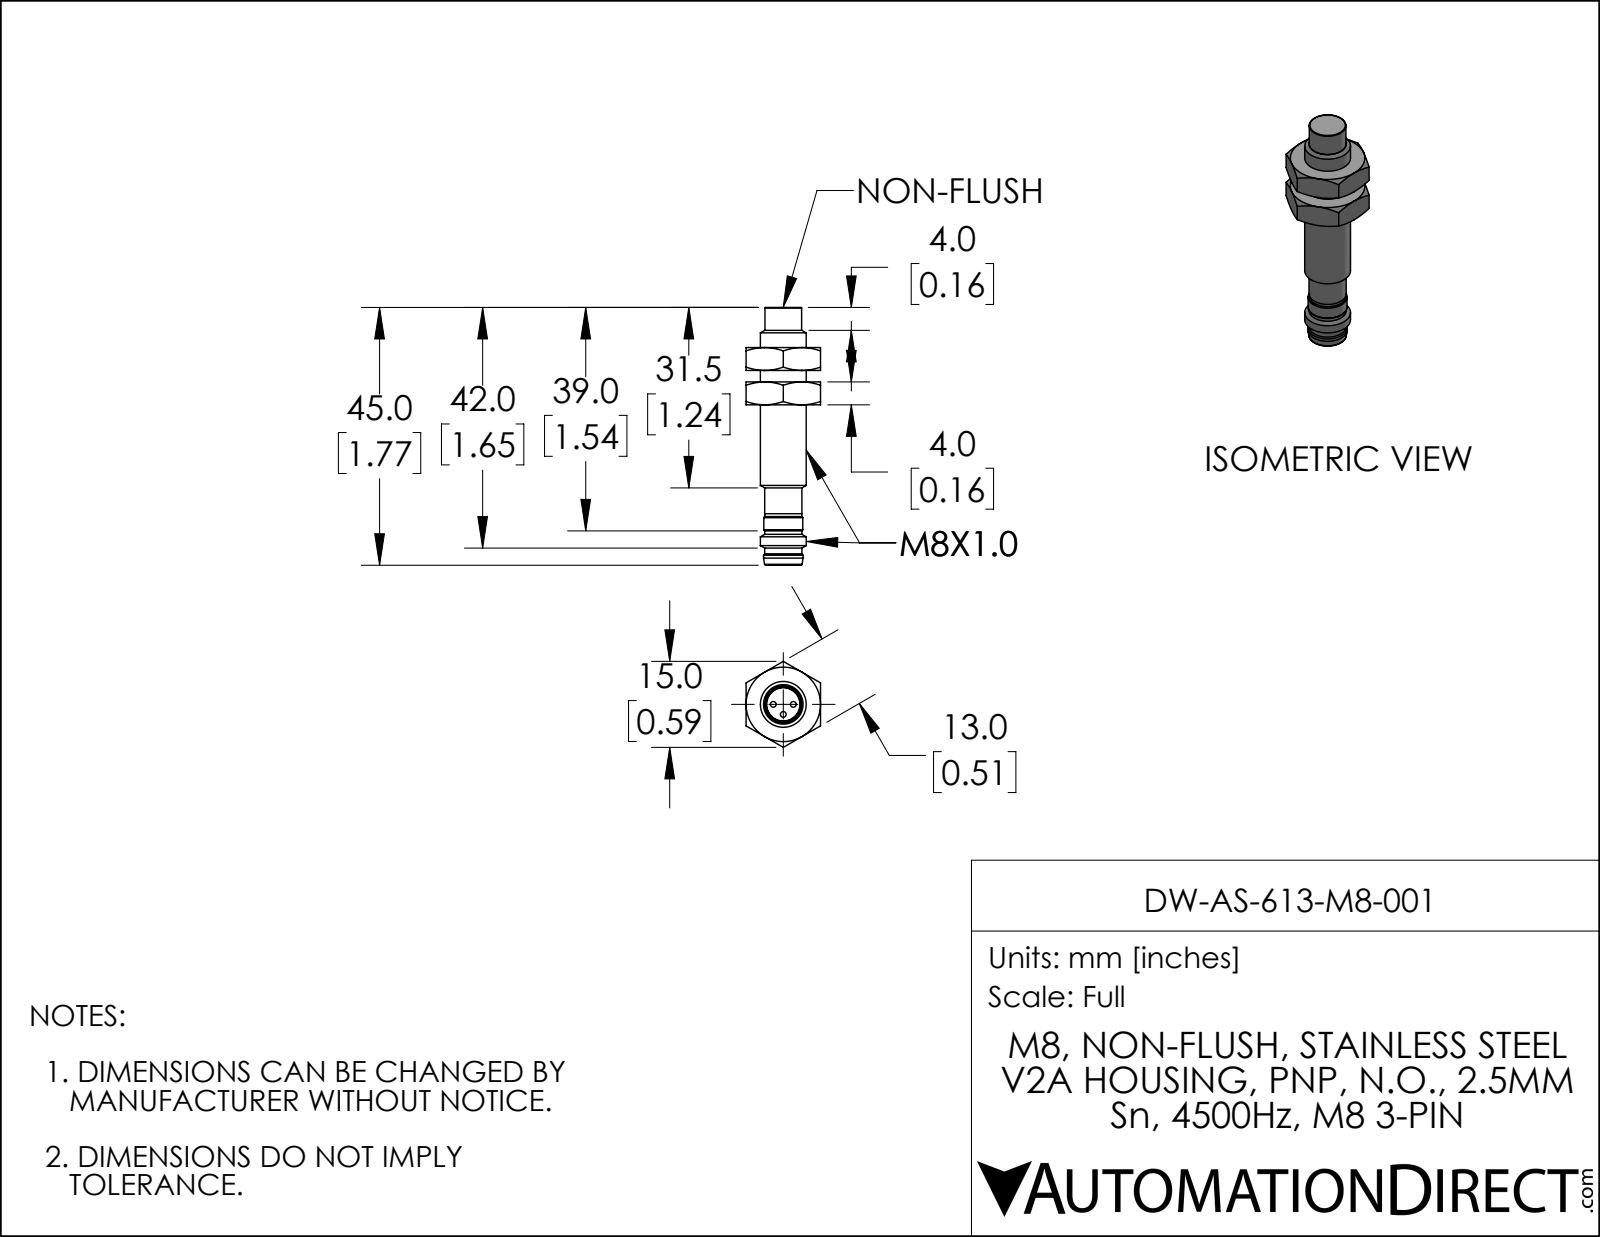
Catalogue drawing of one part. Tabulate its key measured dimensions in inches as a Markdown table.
| quantity | value |
| --- | --- |
| part name | DW-AS-613-M8-001 |
| STEP written by | SolidWorks 2019 (AUTOMOTIVE_DESIGN) |
| units | inches |
| bodies | 1 solid, 76 faces (24 planar, 15 cylindrical, 37 other) |
| overall size | 1.772 × 0.591 × 0.512 |
| volume | 0.161 in³ |
| surface area | 2.817 in² |
| round holes (diameter × count) | 0.228 × 1 |
| round bosses / shafts (diameter × count) | 0.039 × 3, 0.315 × 1, 0.272 × 1, 0.268 × 1, 0.256 × 1, 0.254 × 1, 0.252 × 1 |
| main face-to-face distances | 0.512, 0.157, 0.236, 0.079, 0.394, 0.276, 0.433, 0.669, 1.142, 0.906 |
